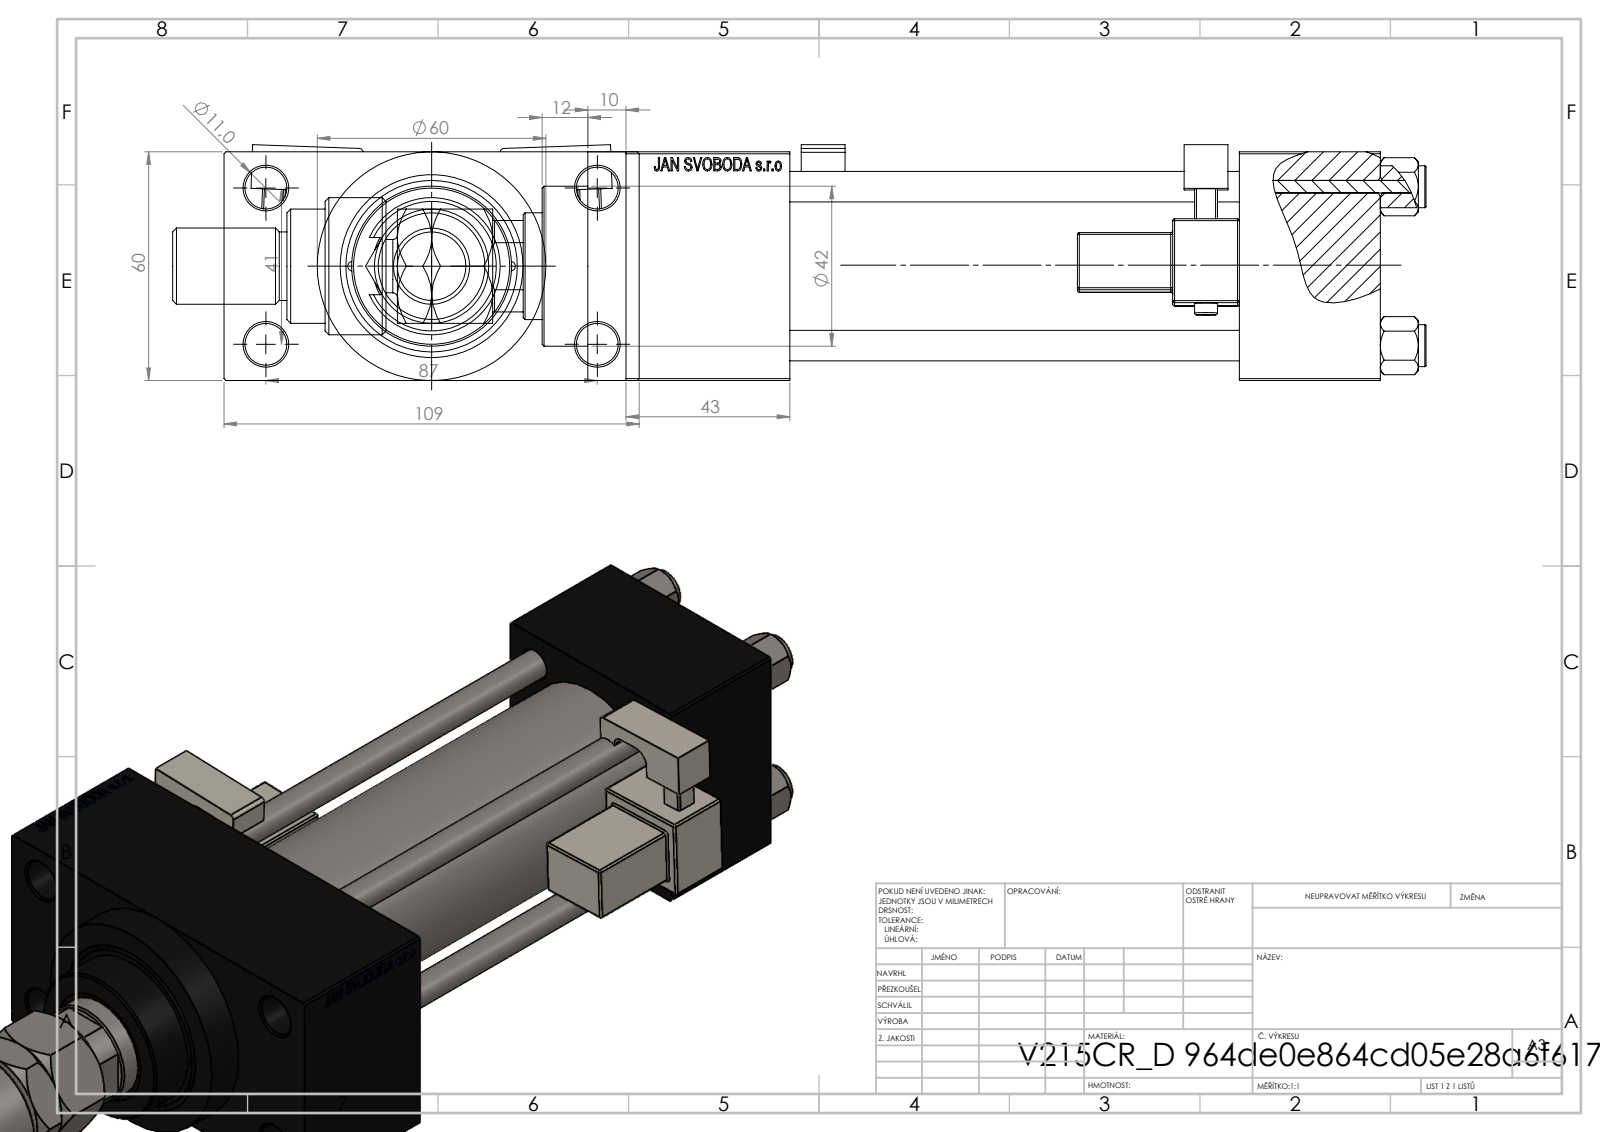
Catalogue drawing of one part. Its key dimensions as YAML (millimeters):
part_name: "MFA; V215CR_D_TYCINKA; FEMALE_PART_FOR_DFA; V215_VC_A (+4 more)"
step_written_by: "SolidWorks 2019 (CONFIG_CONTROL_DESIGN)"
units: millimeters
bodies: {solids: 15, faces: 1353, planar: 588, cylindrical: 165, other: 600}
overall_size: [329, 109, 61.9]
volume: 691744
surface_area: 181926
round_holes:
  - {diameter: 8, count: 4}
  - {diameter: 11, count: 4}
  - {diameter: 2.5, count: 2}
  - {diameter: 7, count: 2}
  - {diameter: 16.66, count: 2}
  - {diameter: 24, count: 2}
  - {diameter: 18.5, count: 1}
  - {diameter: 28, count: 1}
  - {diameter: 31, count: 1}
  - {diameter: 40, count: 1}
  - {diameter: 45, count: 1}
round_bosses_or_shafts:
  - {diameter: 11, count: 4}
  - {diameter: 6, count: 2}
  - {diameter: 60, count: 1}
  - {diameter: 46, count: 1}
  - {diameter: 42, count: 1}
  - {diameter: 36, count: 1}
  - {diameter: 30, count: 1}
  - {diameter: 22, count: 1}
partial_cylinders:
  - {radius: 0.5, count: 48}
  - {radius: 1, count: 2}
  - {radius: 2.5, count: 2}
  - {radius: 4, count: 2}
  - {radius: 7.5, count: 1}
  - {radius: 12, count: 1}
  - {radius: 13.5, count: 1}
face_to_face_distances: [60, 118, 24.5, 84.5, 37, 155, 43, 198, 161, 109]
hole_center_spacings: [20.85, 22.65, 29.49, 30.62, 41.7, 46.53, 47.15, 48.09]
